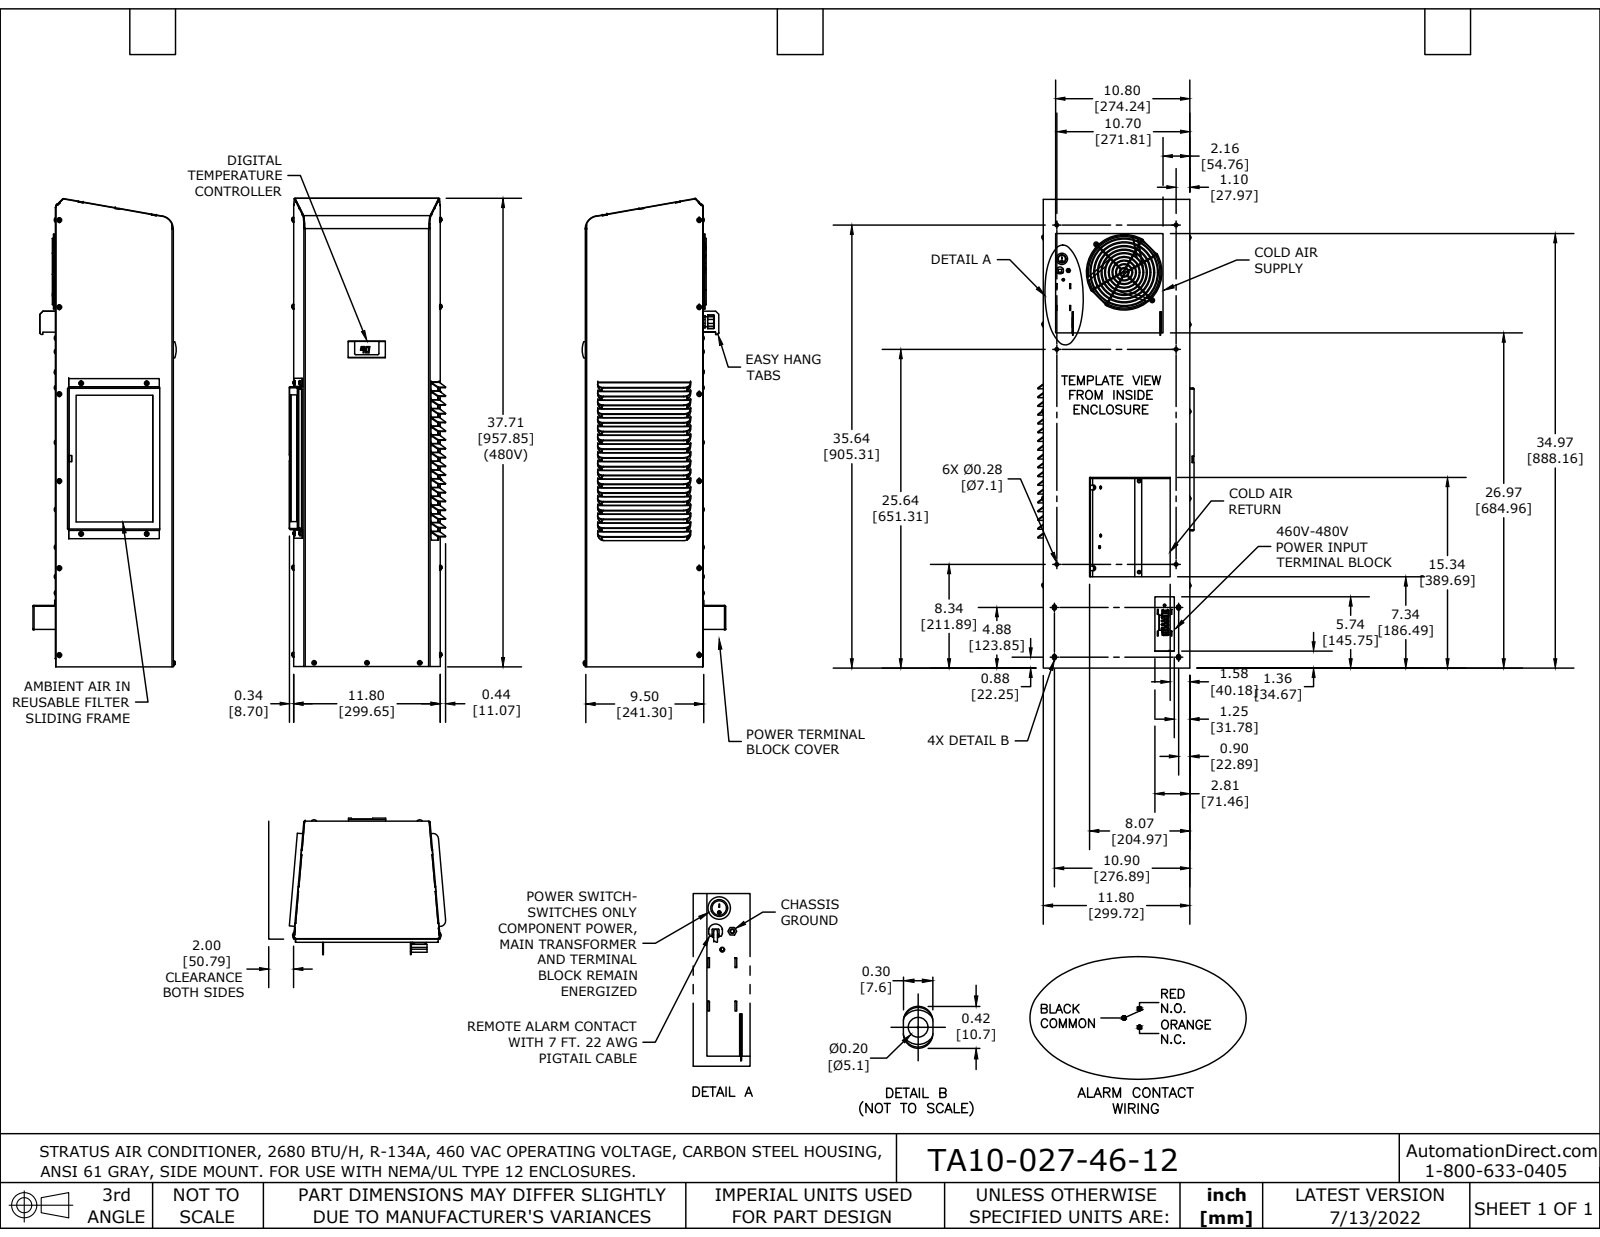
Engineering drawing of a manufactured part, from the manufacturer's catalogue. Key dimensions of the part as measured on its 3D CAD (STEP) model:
Part name (STEP PRODUCT): TA10-027-46-12
STEP written by: SolidWorks 2021 (AUTOMOTIVE_DESIGN)
Units: inches
Bodies: 1 solid, 1740 faces (1073 planar, 497 cylindrical, 170 other)
Overall size (bounding box): 32.024 × 12.576 × 11.549
Volume: 136.5 in³ · Surface area: 3 197 in²
Round holes (diameter × count): ⌀0.159 ×11, ⌀0.204 ×5, ⌀6 ×1
Round bosses / shafts (diameter × count): ⌀0.19 ×7, ⌀0.353 ×2, ⌀0.248 ×2, ⌀6.07 ×1, ⌀0.906 ×1, ⌀0.383 ×1, ⌀0.376 ×1, ⌀0.087 ×1
Partial cylindrical surfaces — rounded edges, fillets, slot ends (radius × count): R0.015 ×45, R0.01 ×42, R0.5 ×36, R0.506 ×36, R0.1 ×28, R0.058 ×21, R0.116 ×21, R0.03 ×13
Main face-to-face distances: 0.058, 9.435, 9.377, 0.058, 9.493, 0.09, 0.25, 0.308, 9.685, 9.743
Hole centre spacings: 7, 14, 21, 1.732, 5.3, 6.565, 12.12, 13.228
